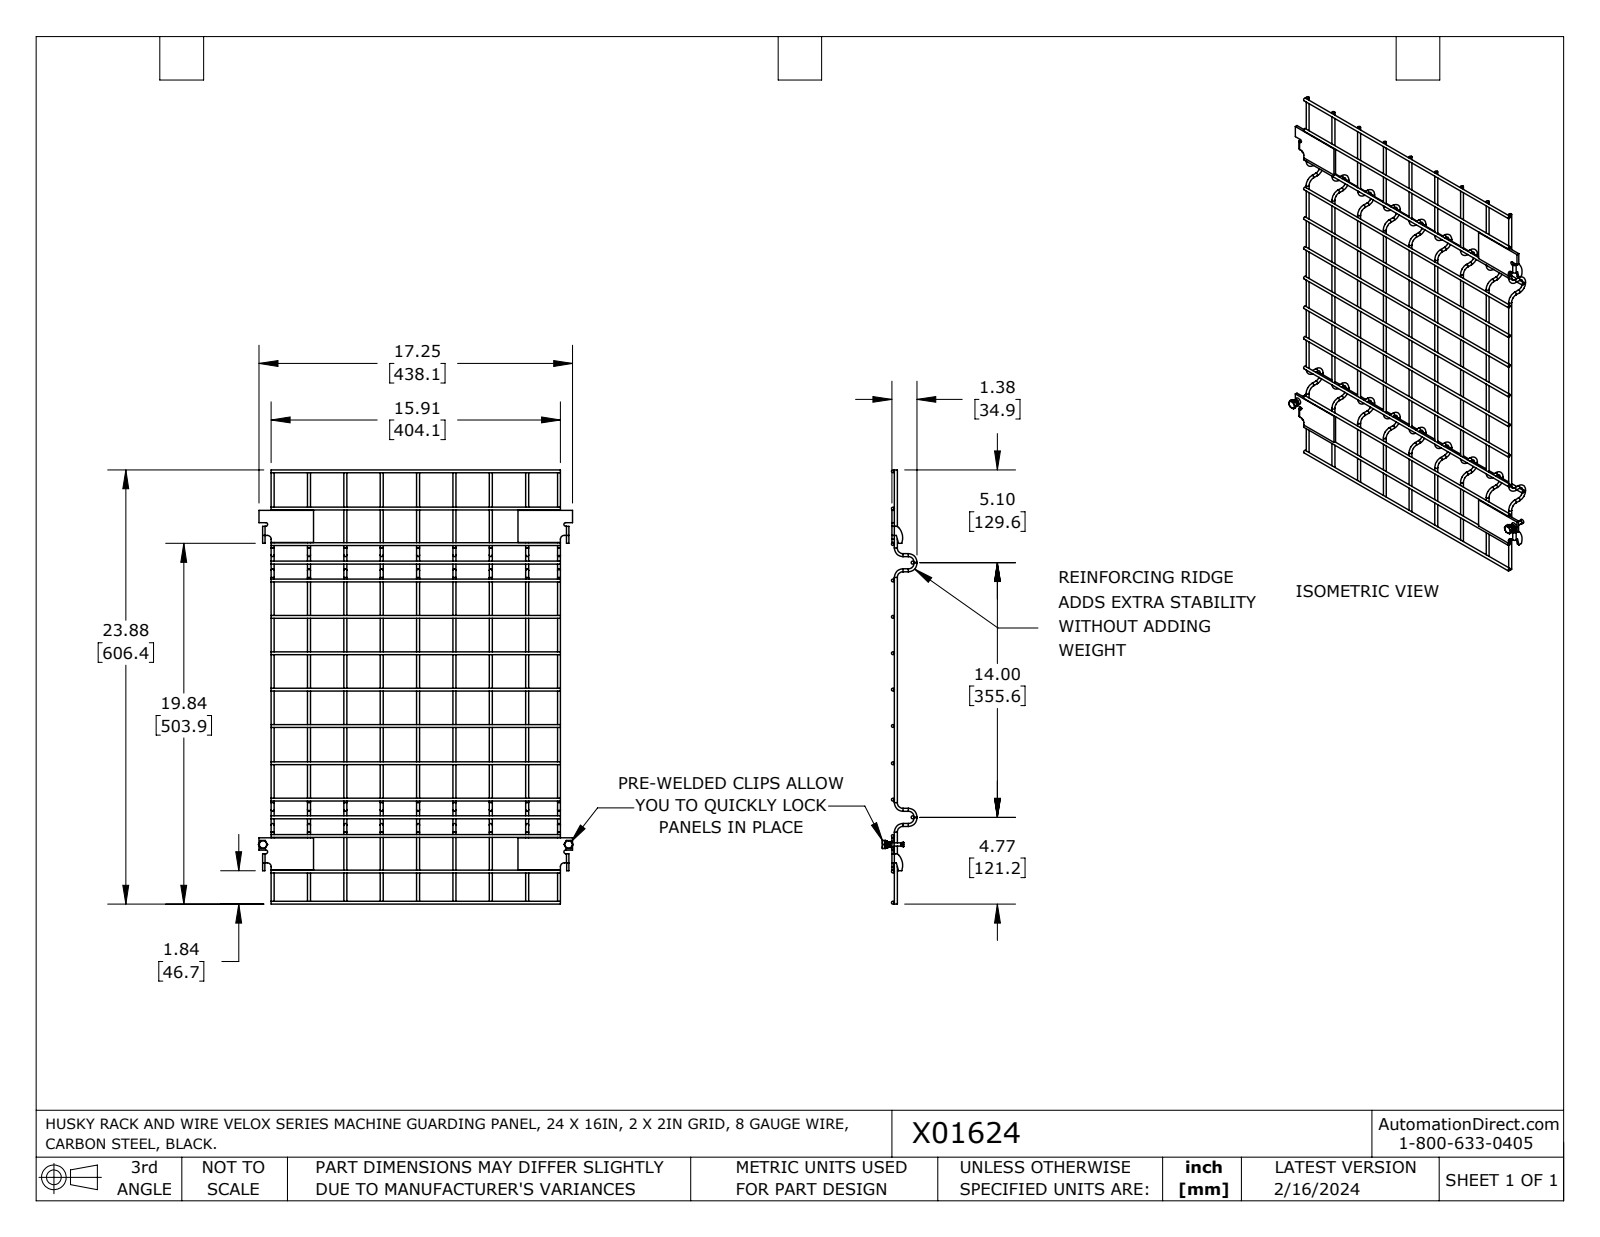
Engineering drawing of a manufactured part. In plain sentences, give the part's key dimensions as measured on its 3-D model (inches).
The part is named "X01624". Its 3-D file was written by "SolidWorks 2023 (AUTOMOTIVE_DESIGN)". It is 32 solids with 356 faces: 128 planar, 132 cylindrical and 96 other. Overall it measures 23.875 by 17.313 by 1.853 inches. Its volume is 12.43 cubic inches and its surface area 292.6 square inches. Round holes: 2 of diameter 0.201, 2 of diameter 0.25. Round bosses or shafts: 69 of diameter 0.16, 2 of diameter 0.39, 2 of diameter 0.245, 2 of diameter 0.187. Partial cylindrical surfaces (rounded edges, fillets, slot ends): 4 of radius 0.1, 4 of radius 0.218, 2 of radius 0.009, 2 of radius 0.067, 2 of radius 0.134, 2 of radius 0.25, 2 of radius 0.865. The main face-to-face distances are 0.134, 0.125, 2.798, 14.046, 18, 18, 0.467, 16.377, 2.331, 13.579. The hole center spacings are 16.808.
